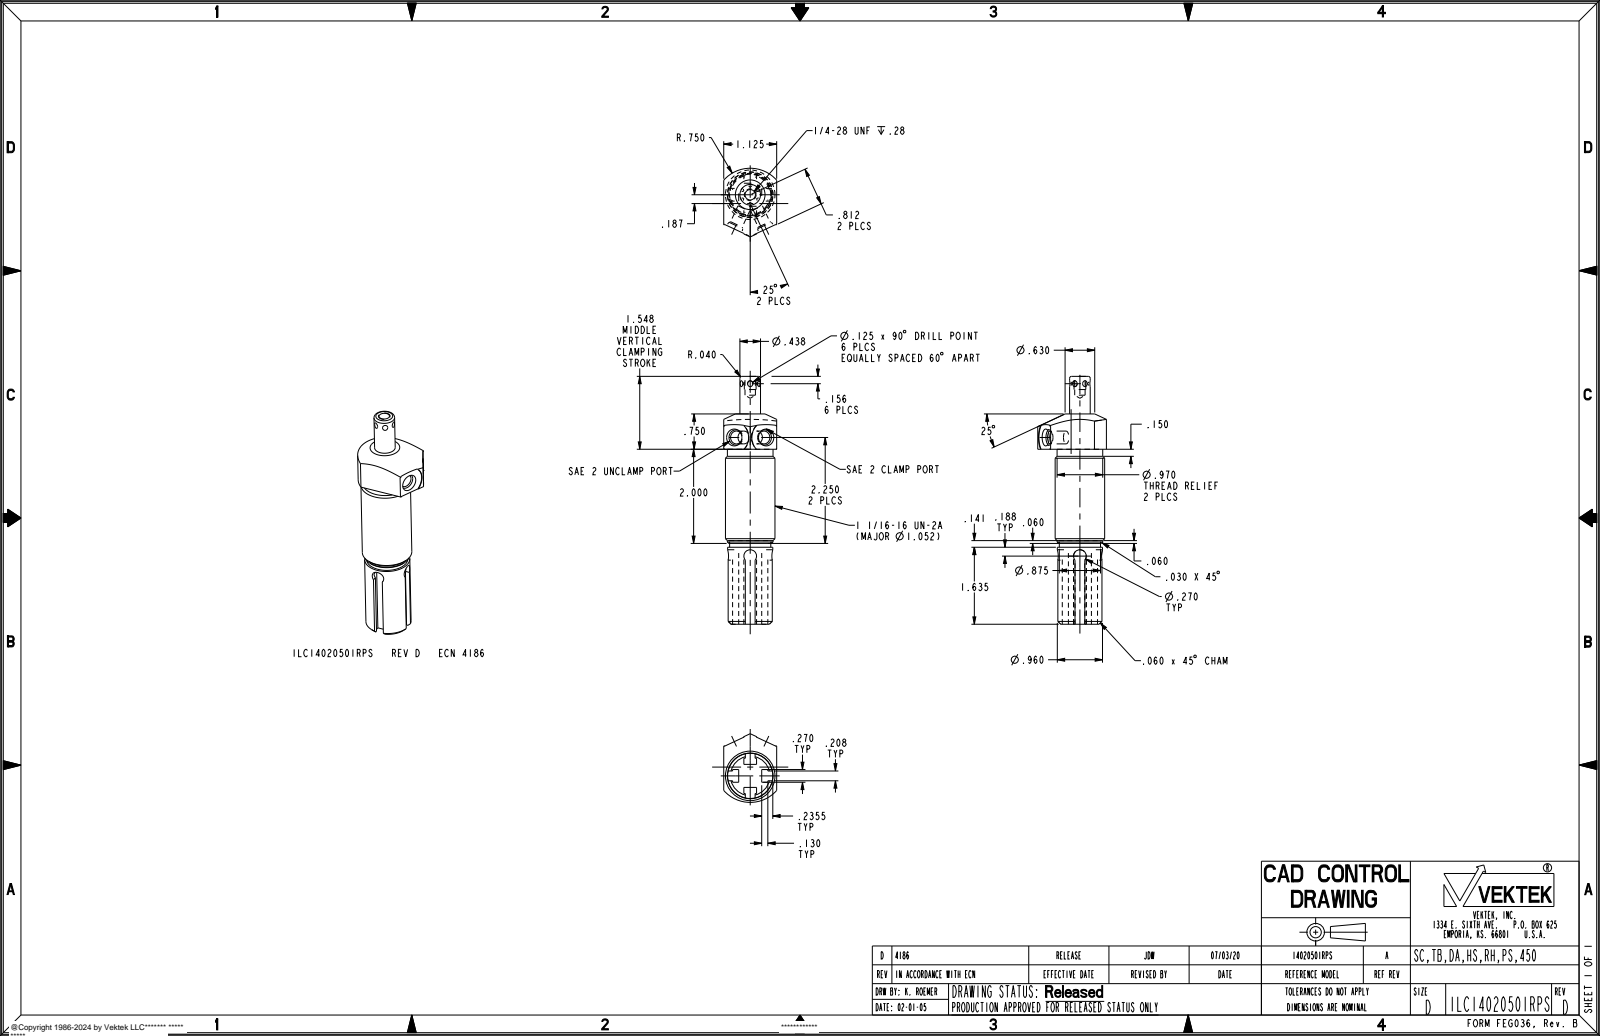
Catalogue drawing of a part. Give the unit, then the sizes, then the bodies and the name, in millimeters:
Units: millimetres
Overall size (bounding box): 133.7 × 37.1 × 28.6
Round holes (diameter × count): ⌀6.9 ×2, ⌀5.6 ×1, ⌀22.7 ×1
Round bosses / shafts (diameter × count): ⌀26.7 ×1, ⌀24.6 ×1, ⌀24.4 ×1, ⌀22.2 ×1, ⌀11.1 ×1, ⌀6.4 ×1
Partial cylindrical surfaces — rounded edges, fillets, slot ends (radius × count): R3.4 ×2, R8.7 ×2, R19.1 ×1
Main face-to-face distances: 2.8, 9.7, 3.6, 8.8, 0.8, 6.1, 8.1, 20.5, 12.4, 6.9
Volume: 58 240 mm³ · Surface area: 15 190 mm²
Bodies: 1 solid, 117 faces (48 planar, 33 cylindrical, 36 other)
Part name (STEP PRODUCT): ILC14020501RPS
STEP written by: PRO/ENGINEER BY PARAMETRIC TECHNOLOGY CORPORATION, 2013320 (AUTOMOTIVE_DESIGN)
